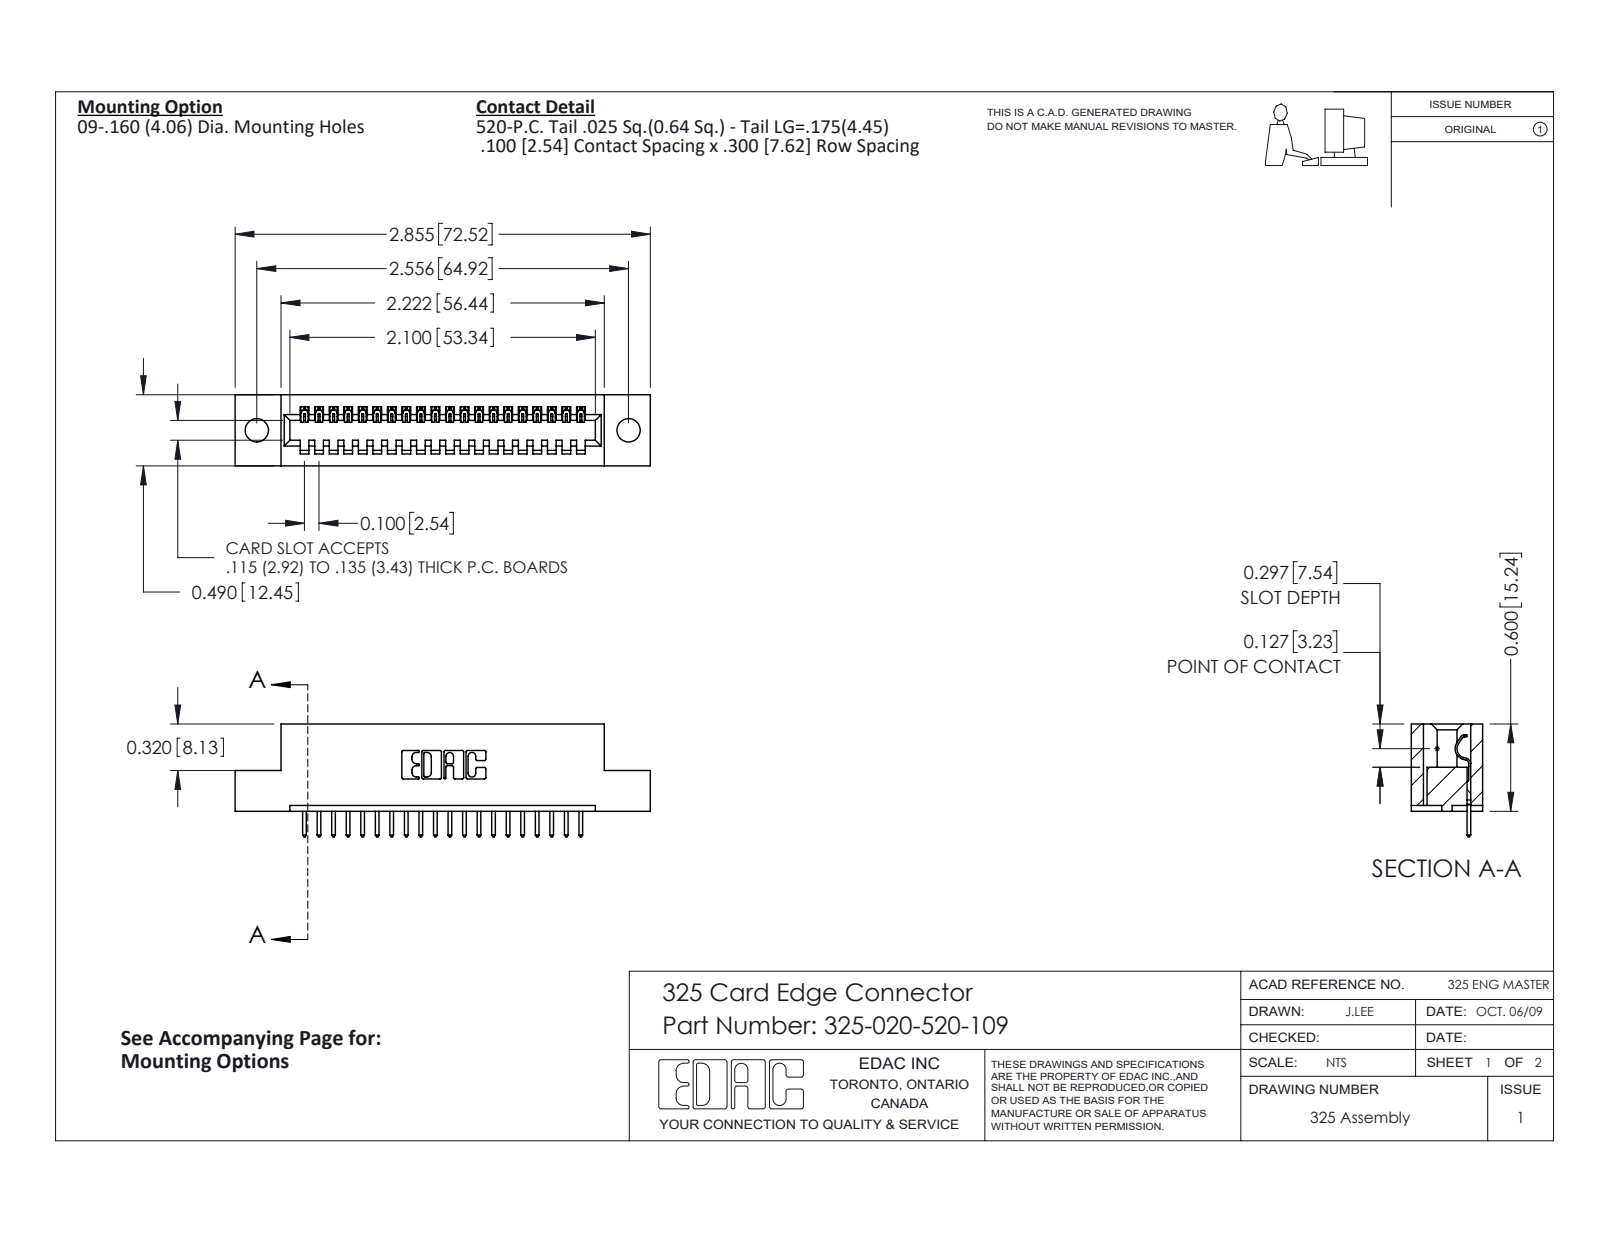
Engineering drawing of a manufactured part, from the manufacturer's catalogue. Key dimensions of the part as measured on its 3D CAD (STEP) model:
Part name (STEP PRODUCT): 325-020-520-109; 325-292-001_325-293-120; 325 Part_.160 TH
STEP written by: SolidWorks 2016 (CONFIG_CONTROL_DESIGN)
Units: inches
Bodies: 21 solids, 1274 faces (910 planar, 364 cylindrical, 0 other)
Overall size (bounding box): 2.855 × 0.775 × 0.49
Volume: 0.534 in³ · Surface area: 13.75 in²
Round holes (diameter × count): ⌀0.16 ×2
Partial cylindrical surfaces — rounded edges, fillets, slot ends (radius × count): R0.006 ×40, R0.01 ×40, R0.01 ×22, R0.007 ×6, R0.031 ×6, R0.026 ×3, R0.014 ×1, R0.022 ×1
Main face-to-face distances: 0.083, 0.407, 0.49, 0.3, 0.107, 0.383, 0.025, 0.04, 0.1, 0.325
Hole centre spacings: 2.556
